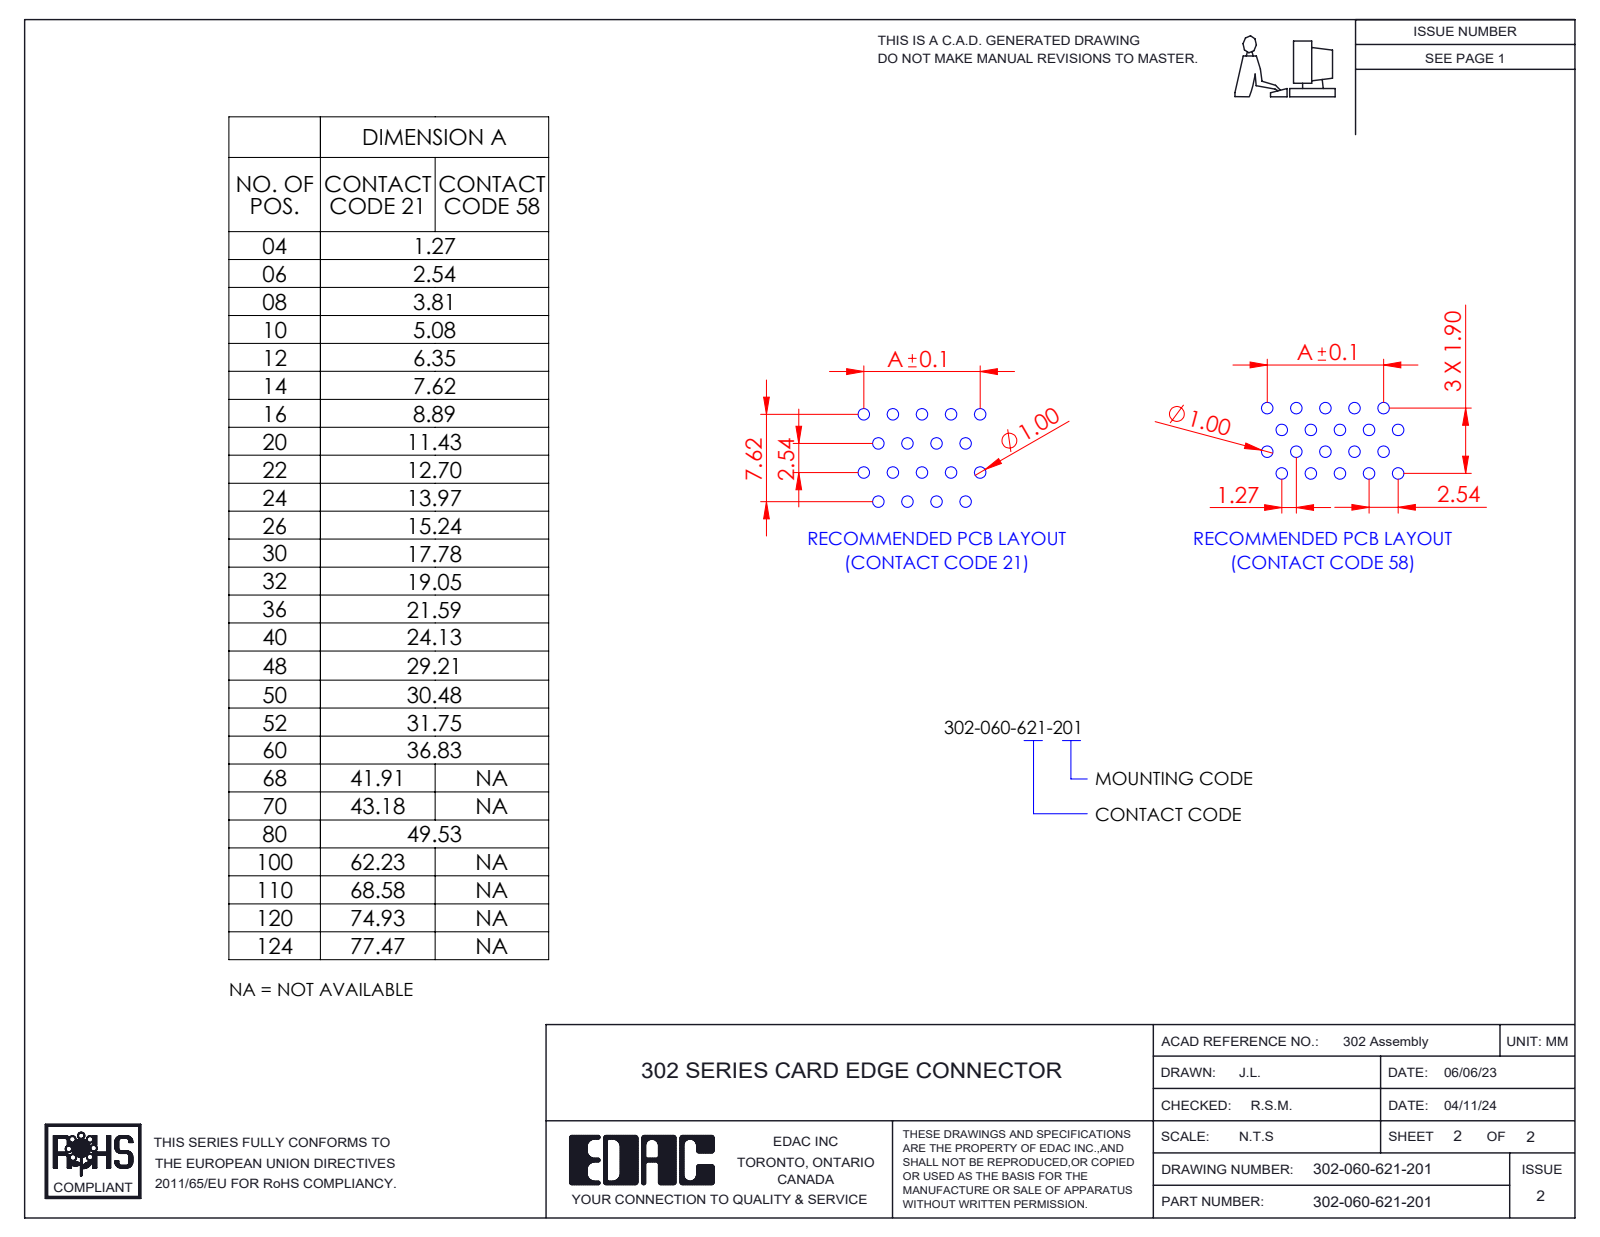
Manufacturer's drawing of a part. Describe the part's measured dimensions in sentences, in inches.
The part is named "HSG_Vertical HSG; Contact_302-290-X21 (2); 302-060-621-201; Contact_302-290-X21 (1)". Its 3-D file was written by "SolidWorks 2023 (CONFIG_CONTROL_DESIGN)". It is 61 solids with 2796 faces: 2059 planar, 613 cylindrical and 124 other. Overall it measures 1.74 by 0.694 by 0.35 inches. Its volume is 0.211 cubic inches and its surface area 14.43 square inches. Partial cylindrical surfaces (rounded edges, fillets, slot ends): 68 of radius 0.008, 4 of radius 0.08, 4 of radius 0.082, 2 of radius 0.004, 2 of radius 0.016, 2 of radius 0.016, 2 of radius 0.049, 2 of radius 0.06. The main face-to-face distances are 0.35, 0.05, 0.1, 0.15, 0.3, 0.2, 0.15, 0.25, 0.2, 0.3.
